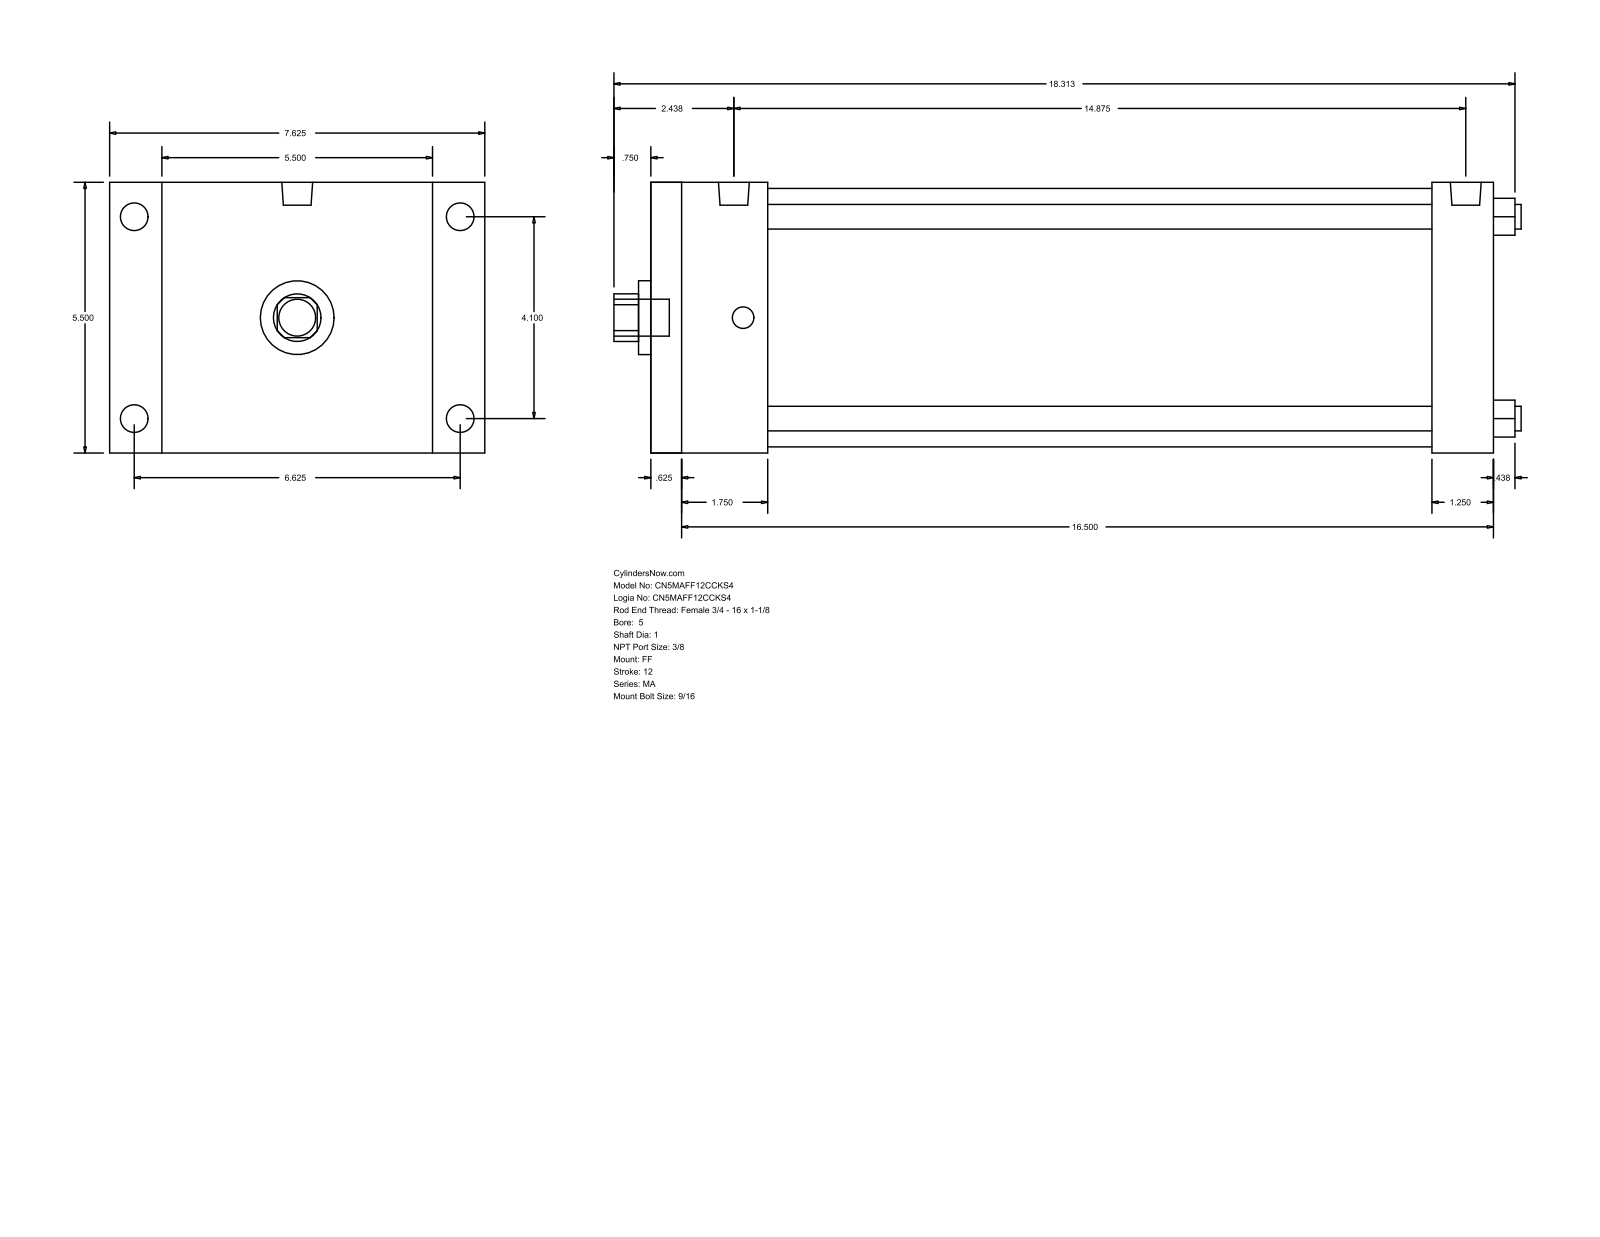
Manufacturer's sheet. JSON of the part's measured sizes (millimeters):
{"part_name": "MA_FF__0500_1", "step_written_by": "GSSL Pune (CONFIG_CONTROL_DESIGN)", "units": "millimeters", "bodies": {"solids": 0, "faces": 92, "planar": 64, "cylindrical": 28, "other": 0}, "overall_size": [468.31, 193.68, 139.7], "round_holes": [[12.7, 4], [25.4, 1], [38.1, 1], [133.35, 1]], "round_bosses_or_shafts": [[14.29, 4], [11.11, 4], [15.93, 2], [19.05, 1]], "partial_cylinders_radius": [[12.29, 1]], "face_to_face_distances": [139.7, 434.97, 15.87, 419.1, 403.22, 387.35, 31.75, 60.33, 44.46, 342.89], "hole_center_spacings": [73.64, 104.14, 147.28]}
